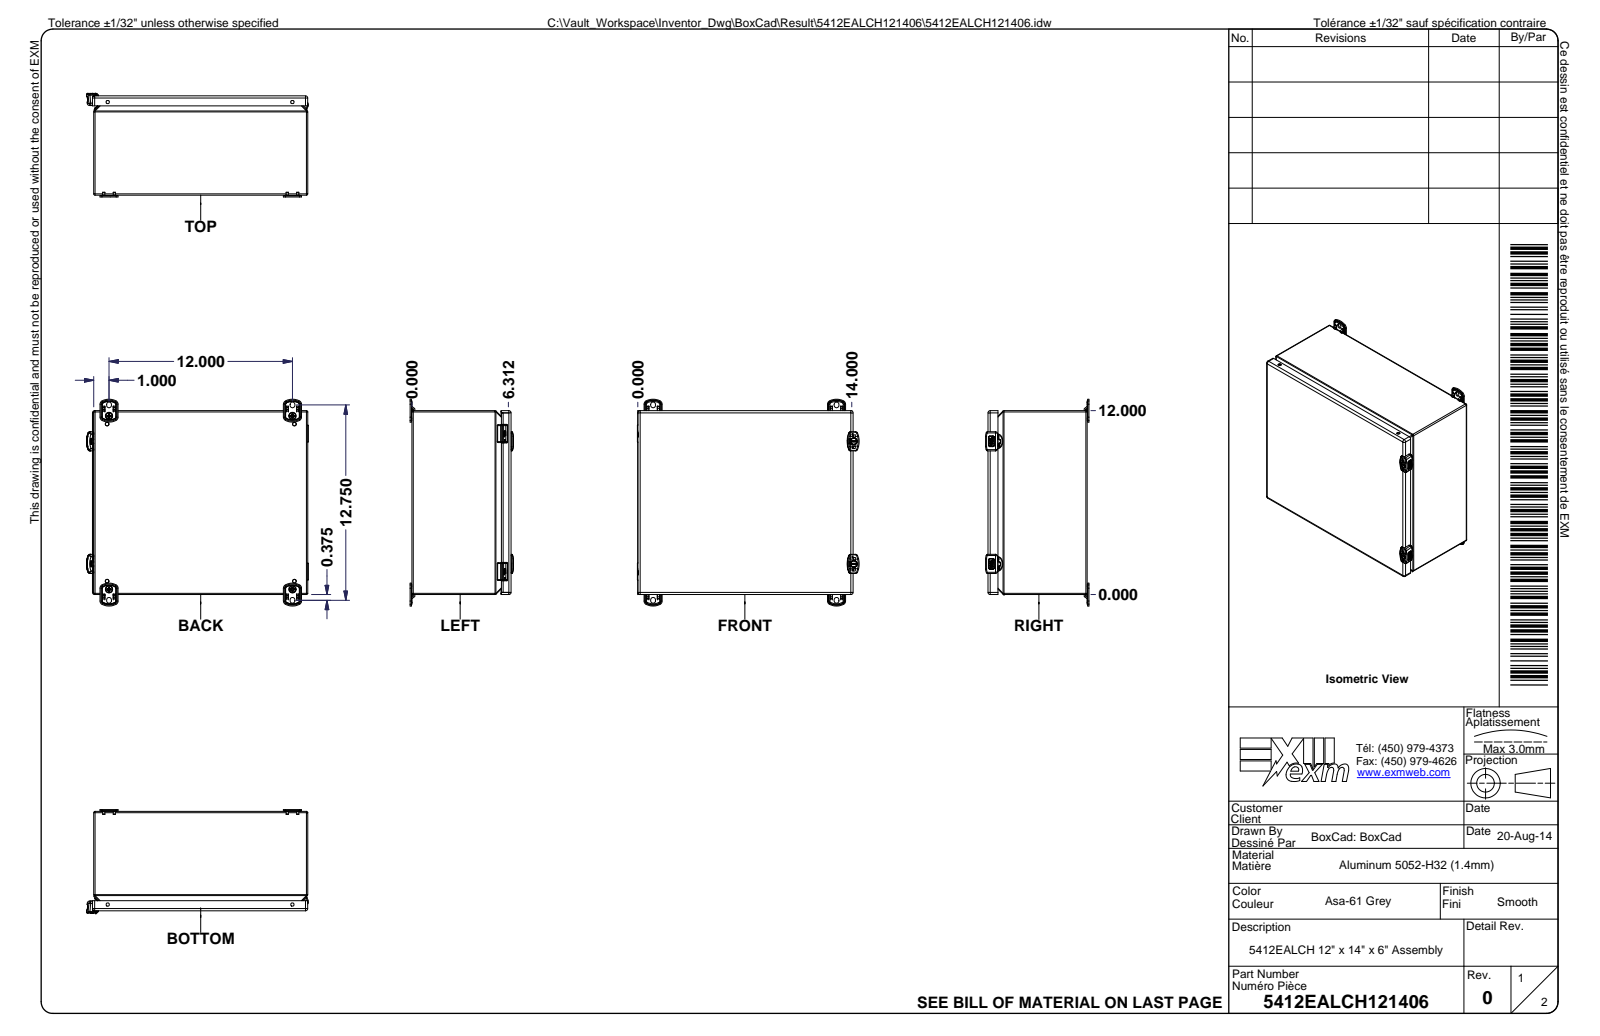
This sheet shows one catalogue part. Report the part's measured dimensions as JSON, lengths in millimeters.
{"part_name": "5412EALCH121406; 5412EALCH121406B; 5412EALCH121406B-P; STK-A-70469-1 (+8 more)", "step_written_by": "Autodesk Inventor 2020 (AUTOMOTIVE_DESIGN)", "units": "millimeters", "bodies": {"solids": 59, "faces": 8409, "planar": 3583, "cylindrical": 2002, "other": 2824}, "overall_size": [368.4, 342.8, 171.7], "volume_mm3": 843800, "surface_area_mm2": 1181000, "round_holes": [[4.2, 4], [4.4, 4], [5, 4], [5, 4], [6, 4], [6, 4], [8.1, 4], [0.8, 2], [4.4, 2], [5.1, 2], [6.1, 2], [8.6, 2]], "round_bosses_or_shafts": [[5.9, 8], [12.7, 4], [7.6, 4], [6, 4], [4.9, 4], [5, 3], [10.5, 2], [10, 2]], "partial_cylinders_radius": [[0.5, 257], [0.3, 209], [1, 92], [0.1, 64], [0.2, 60], [1.5, 57], [0.8, 35], [0.1, 33]], "face_to_face_distances": [1.3, 1.3, 163.4, 162.1, 303.5, 164.7, 163.4, 6, 7.7, 9.1], "hole_center_spacings": [13.9, 203.2, 273.8, 228.6, 308.3, 311.2, 405.7, 412.1]}
